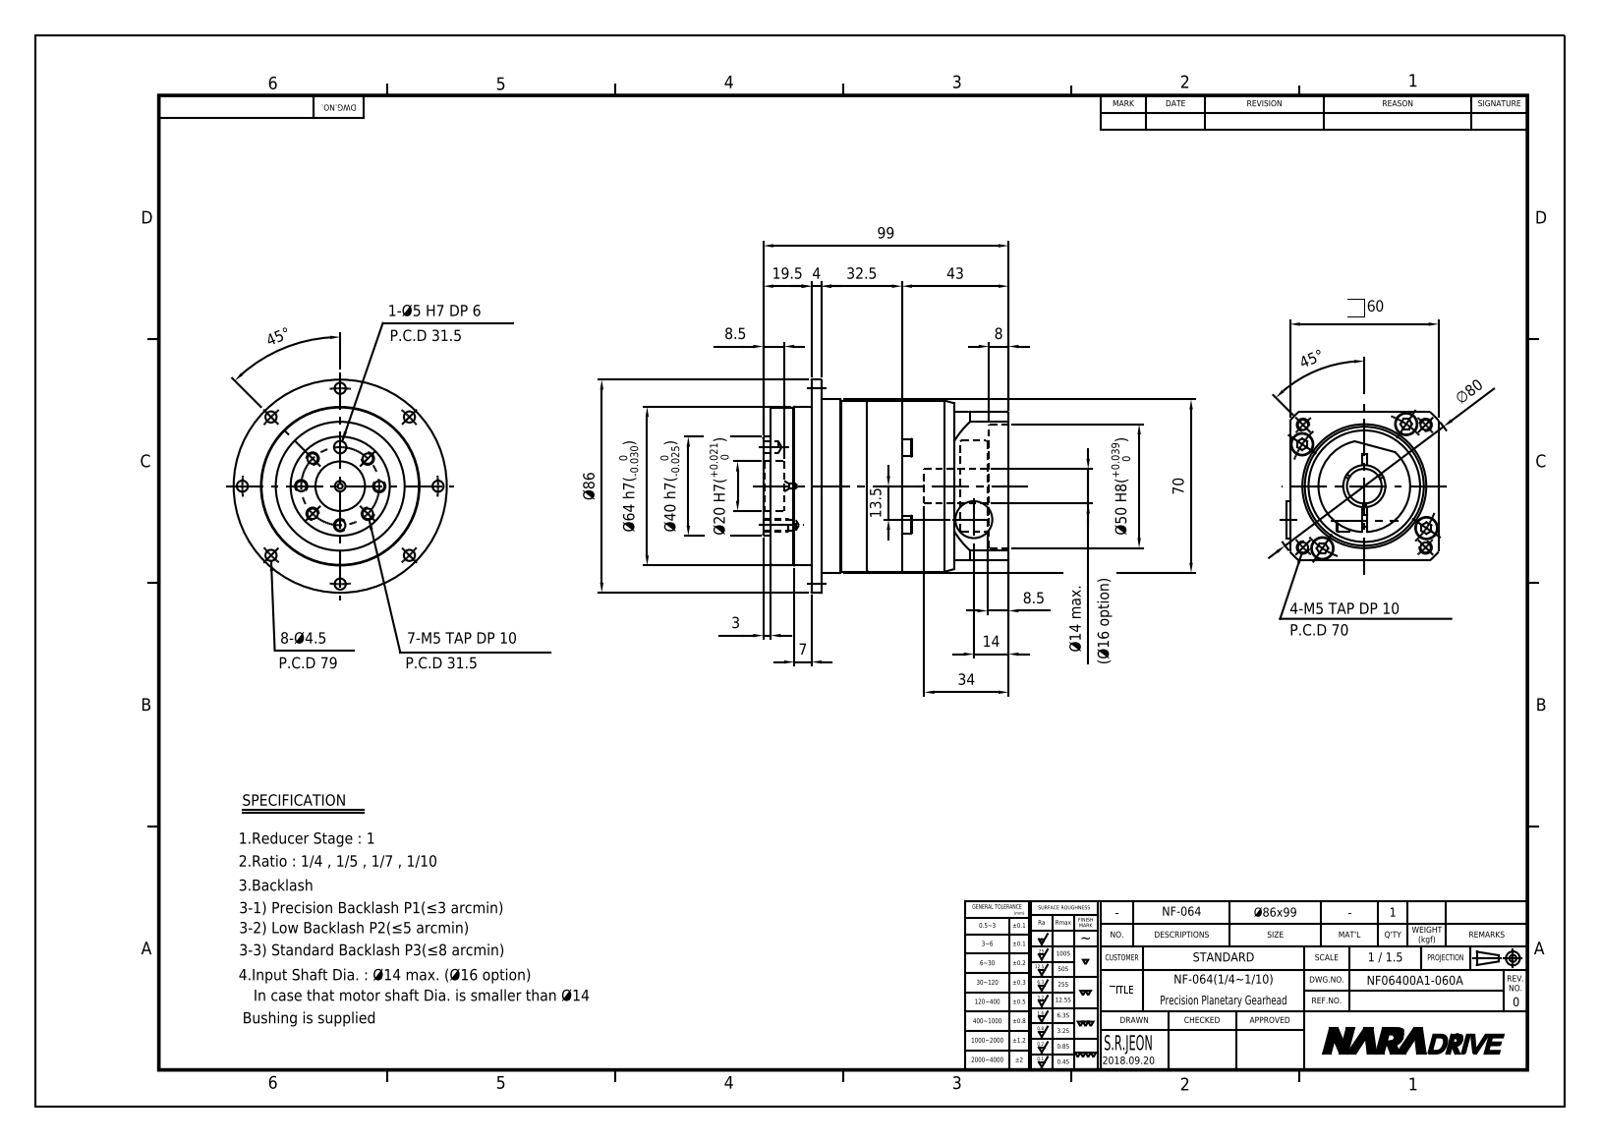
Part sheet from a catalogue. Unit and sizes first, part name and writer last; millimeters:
Units: millimetres
Overall size (bounding box): 99 × 86 × 86
Round holes (diameter × count): ⌀4.13 ×16, ⌀4.5 ×8, ⌀3.24 ×6, ⌀5.5 ×5, ⌀9 ×4, ⌀2 ×1, ⌀5 ×1, ⌀7 ×1, ⌀8.5 ×1, ⌀14 ×1, ⌀17 ×1, ⌀20 ×1
Round bosses / shafts (diameter × count): ⌀8.5 ×5, ⌀5 ×5, ⌀86 ×1, ⌀70 ×1, ⌀69 ×1, ⌀64 ×1, ⌀63.5 ×1, ⌀43.5 ×1
Partial cylindrical surfaces — rounded edges, fillets, slot ends (radius × count): R4 ×6, R4.25 ×6, R0.5 ×4, R4.5 ×1, R40 ×1
Main face-to-face distances: 19.5, 8, 3, 22.5, 60, 69, 52.5, 30, 4, 19
Hole centre spacings: 31, 15.75, 23.75, 28.81, 29.1, 30.23, 30.31, 39.5
Volume: 258 870 mm³ · Surface area: 66 957 mm²
Bodies: 1 solid, 398 faces (196 planar, 101 cylindrical, 101 other)
Part name (STEP PRODUCT): NF06400A1-060A
STEP written by: Autodesk Inventor 2016 (AUTOMOTIVE_DESIGN)
